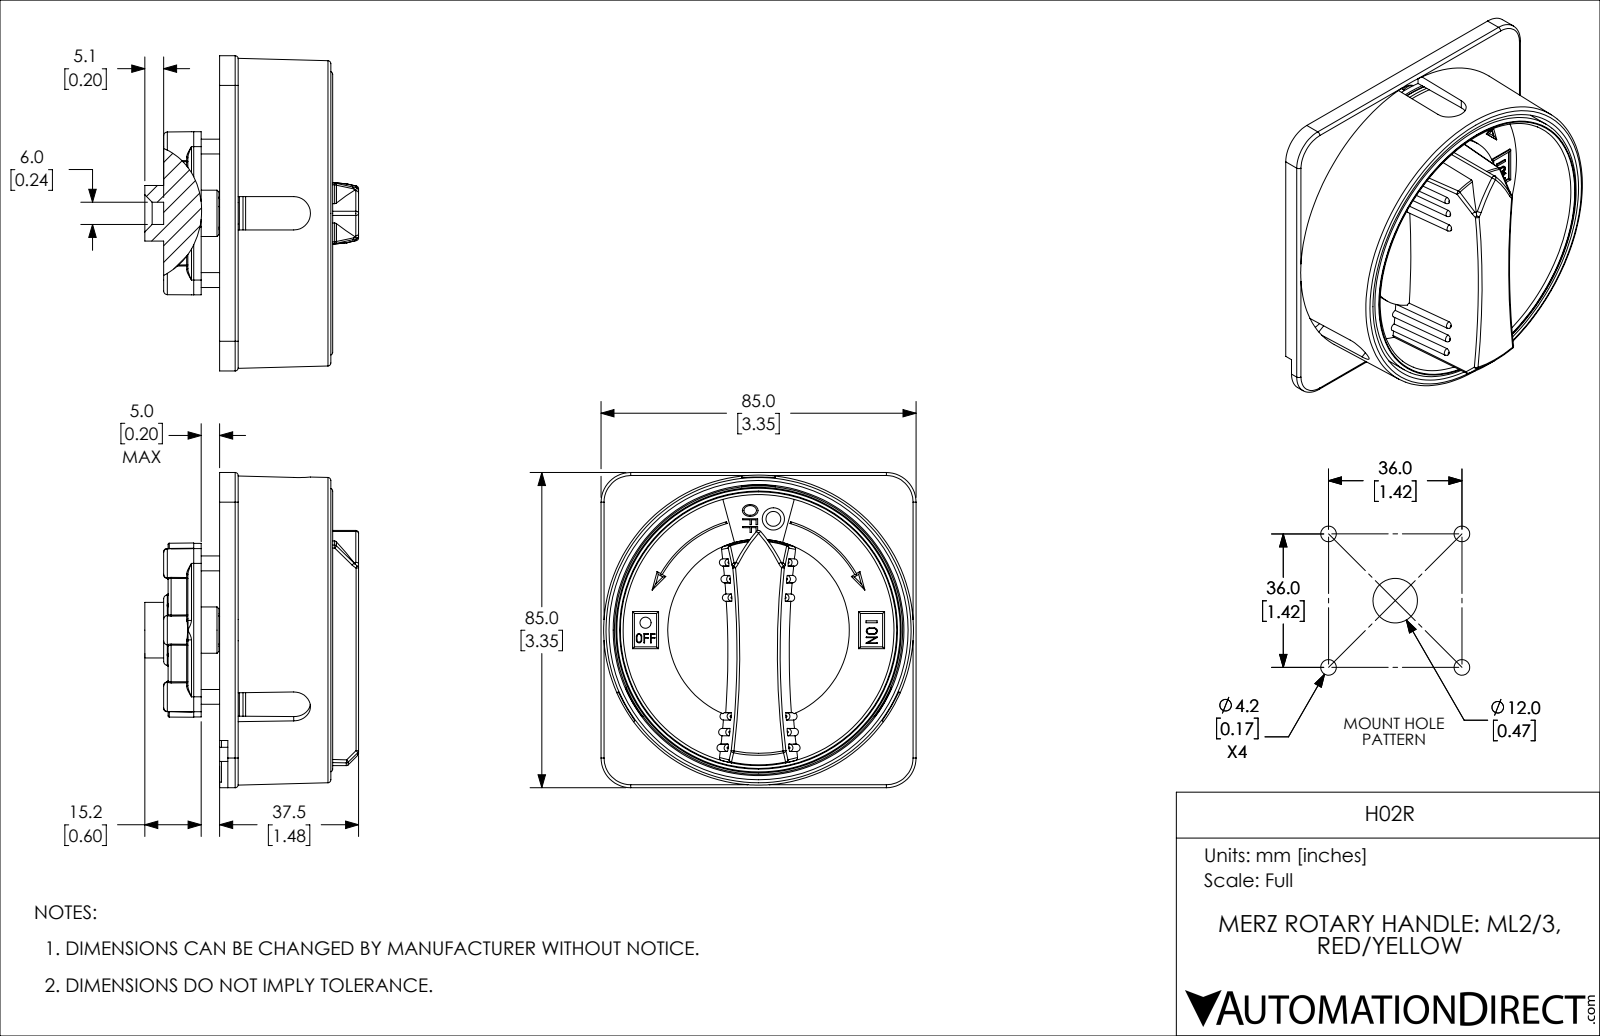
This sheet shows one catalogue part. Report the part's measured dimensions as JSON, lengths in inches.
{"part_name": "H02R", "step_written_by": "SolidWorks 2019 (AUTOMOTIVE_DESIGN)", "units": "inches", "bodies": {"solids": 1, "faces": 1545, "planar": 504, "cylindrical": 291, "other": 750}, "overall_size": [3.346, 3.346, 2.272], "volume_in3": 5.352, "surface_area_in2": 103.5, "round_holes": [[0.236, 1], [0.807, 1], [1.772, 1], [2.878, 1]], "round_bosses_or_shafts": [[0.197, 6], [0.157, 5], [3.031, 1], [3.012, 1], [1.929, 1], [1.87, 1], [1.024, 1], [0.591, 1]], "partial_cylinders_radius": [[0.012, 48], [0.031, 24], [0.01, 14], [0.055, 5], [0.315, 5], [0.039, 4], [0.059, 4], [0.118, 4]], "face_to_face_distances": [0.138, 0.079, 0.217, 0.059, 0.028, 0.11, 0.256, 0.354, 0.177, 0.335], "hole_center_spacings": [1.192]}
